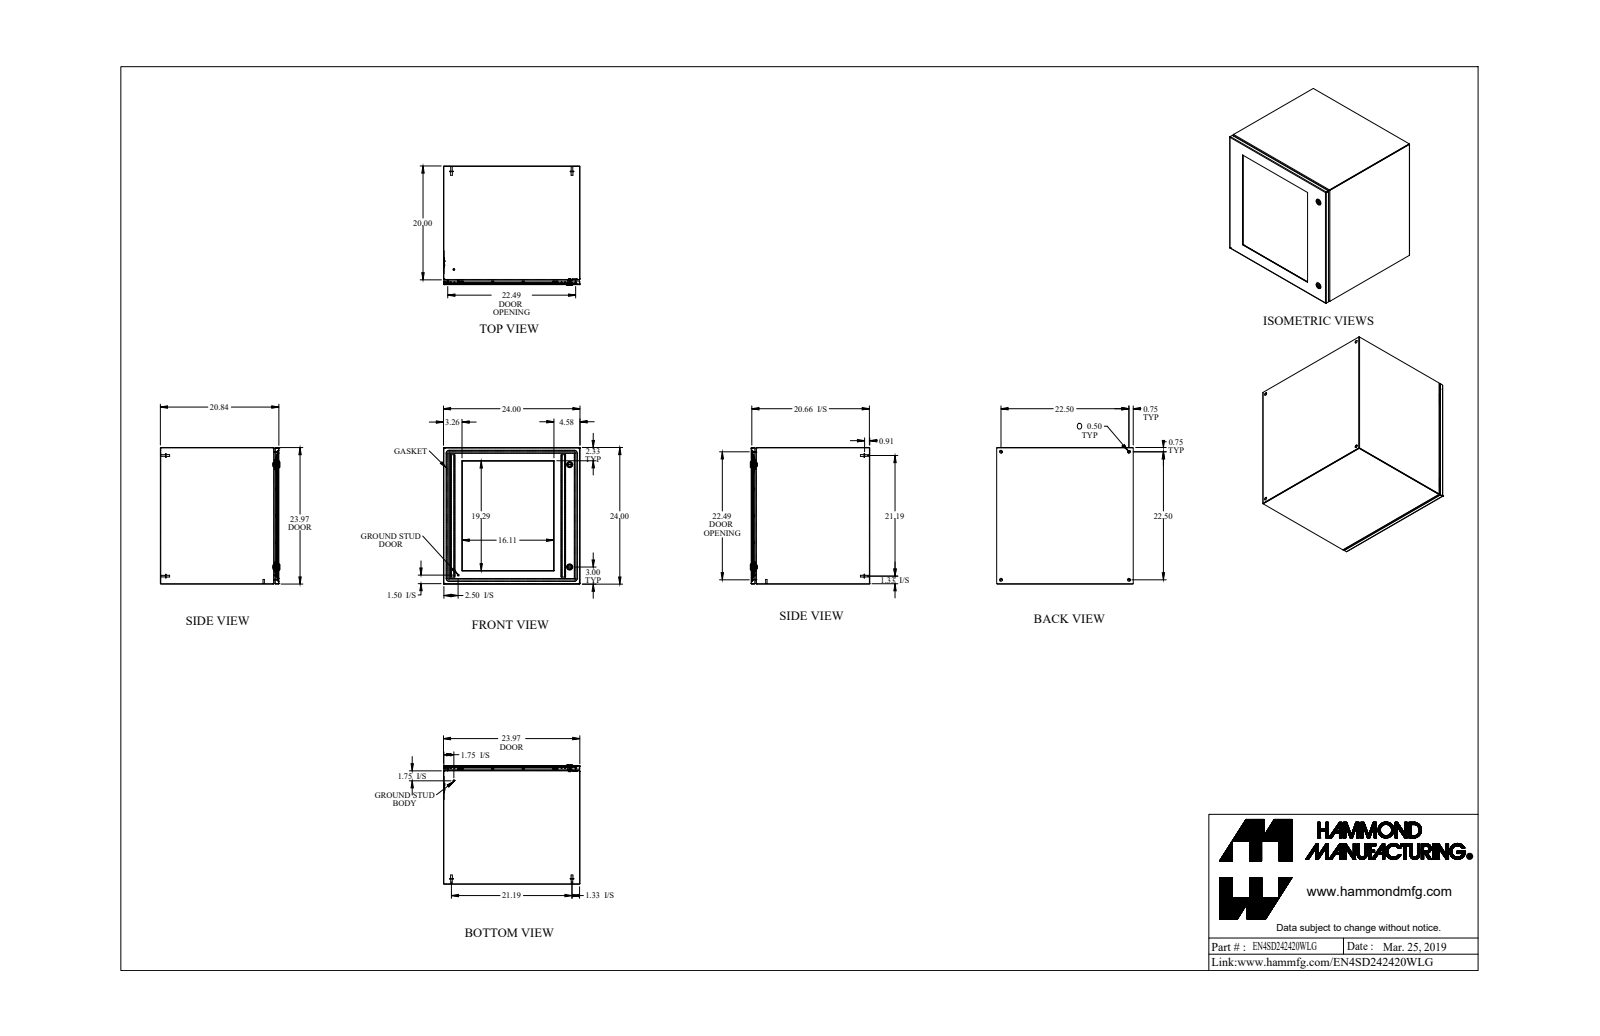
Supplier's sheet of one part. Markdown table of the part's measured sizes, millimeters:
| quantity | value |
| --- | --- |
| part name | EN4SD242420WLG |
| STEP written by | SolidWorks 2019 (AUTOMOTIVE_DESIGN) |
| units | millimeters |
| bodies | 74 solids, 1435 faces (740 planar, 441 cylindrical, 254 other) |
| overall size | 609.6 × 609.6 × 533.3 |
| volume | 5 131 000 mm³ |
| surface area | 4 636 000 mm² |
| round holes (diameter × count) | 3.3 × 18, 6.4 × 18, 12.7 × 4, 5.9 × 2, 15.9 × 2, 19.9 × 2, 4.4 × 1, 6.1 × 1, 6.1 × 1 |
| round bosses / shafts (diameter × count) | 5.7 × 19, 9.3 × 18, 4.2 × 18, 15.9 × 4, 8 × 4, 6.9 × 4, 27.9 × 2, 13.3 × 2 |
| partial cylindrical surfaces (radius × count) | 0.9 × 14, 2.7 × 14, 1.1 × 12, 2.1 × 12, 3.2 × 12, 7.9 × 12, 2.5 × 8, 0.2 × 4 |
| main face-to-face distances | 1.8, 607.8, 605.9, 609.6, 527.4, 525.6, 519.3, 6.4, 521.1, 8.2 |
| hole center spacings | 136.4, 451.6, 119.9, 497.1, 534.2, 136.4, 239.7, 272.9 |
